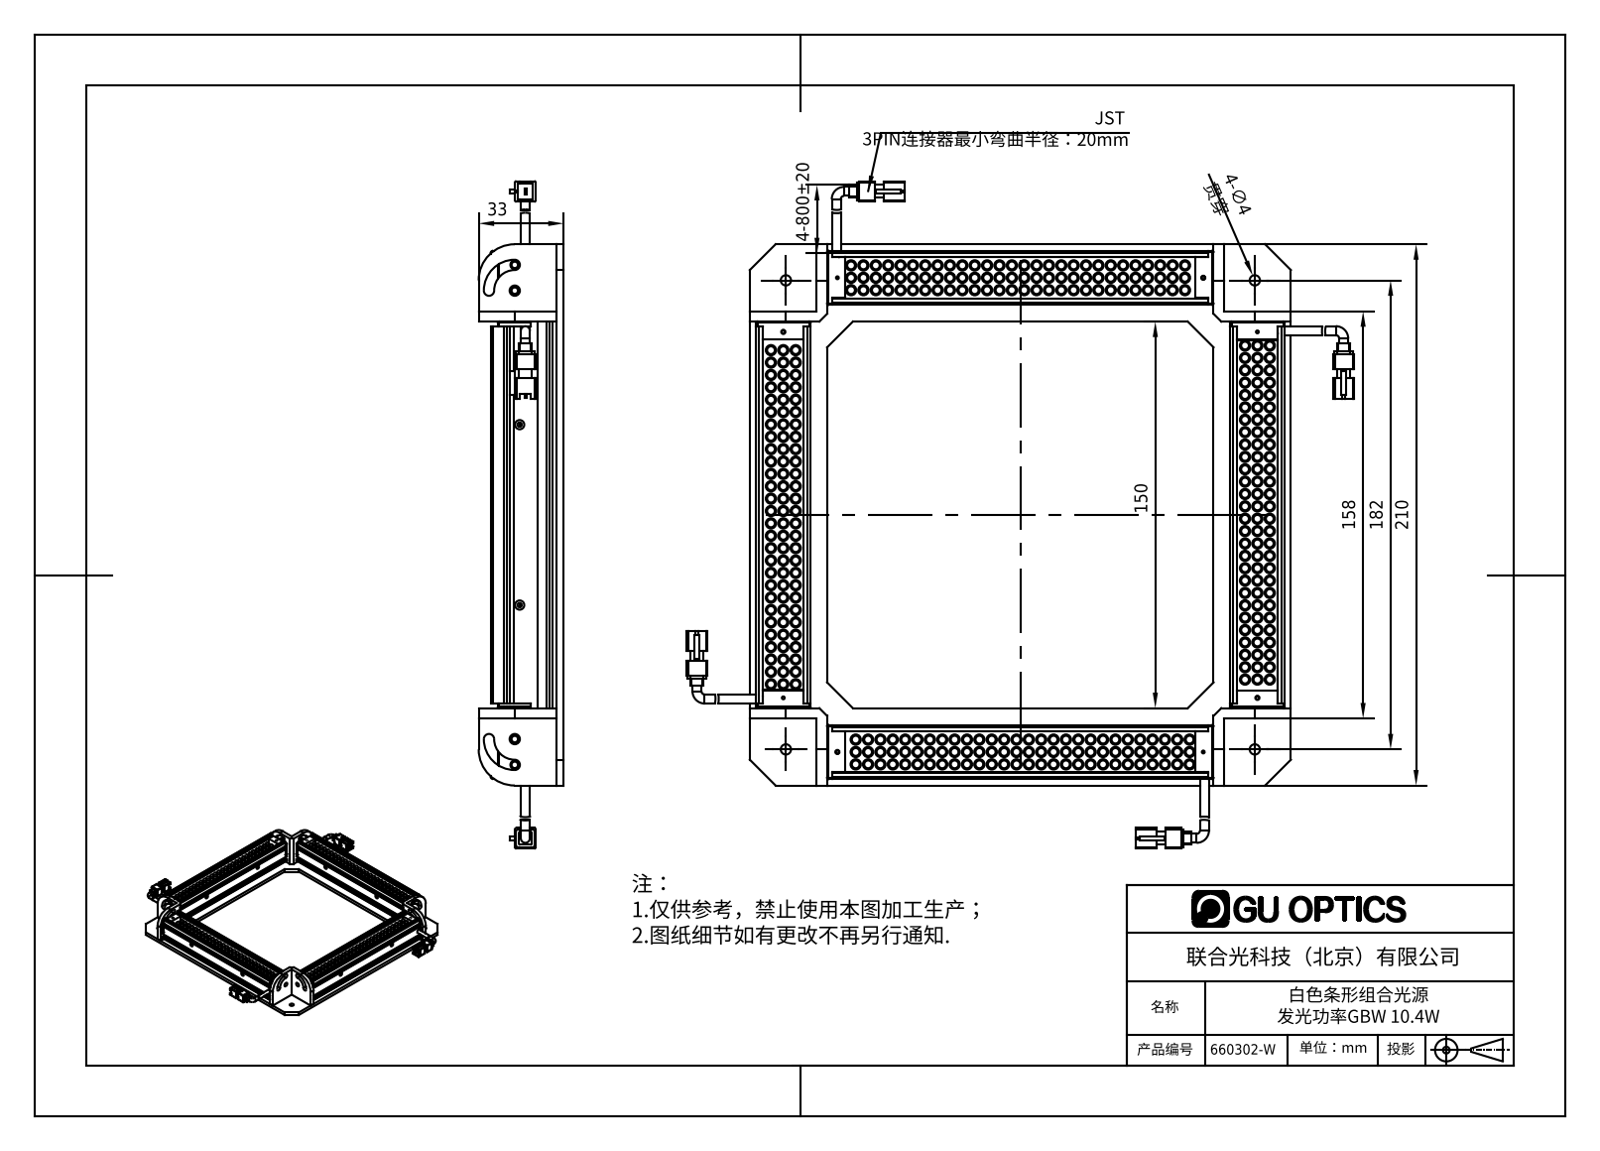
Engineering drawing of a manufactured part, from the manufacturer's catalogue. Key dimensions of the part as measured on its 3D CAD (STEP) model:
Part name (STEP PRODUCT): 660302-W
STEP written by: SolidWorks 2016 (AUTOMOTIVE_DESIGN)
Units: millimetres
Bodies: 29 solids, 3465 faces (1176 planar, 1712 cylindrical, 577 other)
Overall size (bounding box): 259 × 259 × 33
Volume: 238 480 mm³ · Surface area: 215 116 mm²
Round holes (diameter × count): ⌀1.6 ×12, ⌀2.5 ×8, ⌀3 ×8, ⌀4 ×8, ⌀1.1 ×4, ⌀1.25 ×4, ⌀1.7 ×4, ⌀2 ×4
Round bosses / shafts (diameter × count): ⌀4 ×336, ⌀3 ×336, ⌀3.5 ×8
Partial cylindrical surfaces — rounded edges, fillets, slot ends (radius × count): R1 ×48, R0.5 ×32, R2 ×8, R1.65 ×4, R8 ×4, R12 ×4, R14 ×4
Main face-to-face distances: 2.5, 3, 184, 18.5, 21, 4, 1, 181.5, 9.9, 6.5
Hole centre spacings: 16.38, 20.02, 26.23, 142, 158.04, 162, 164.35, 168.04
